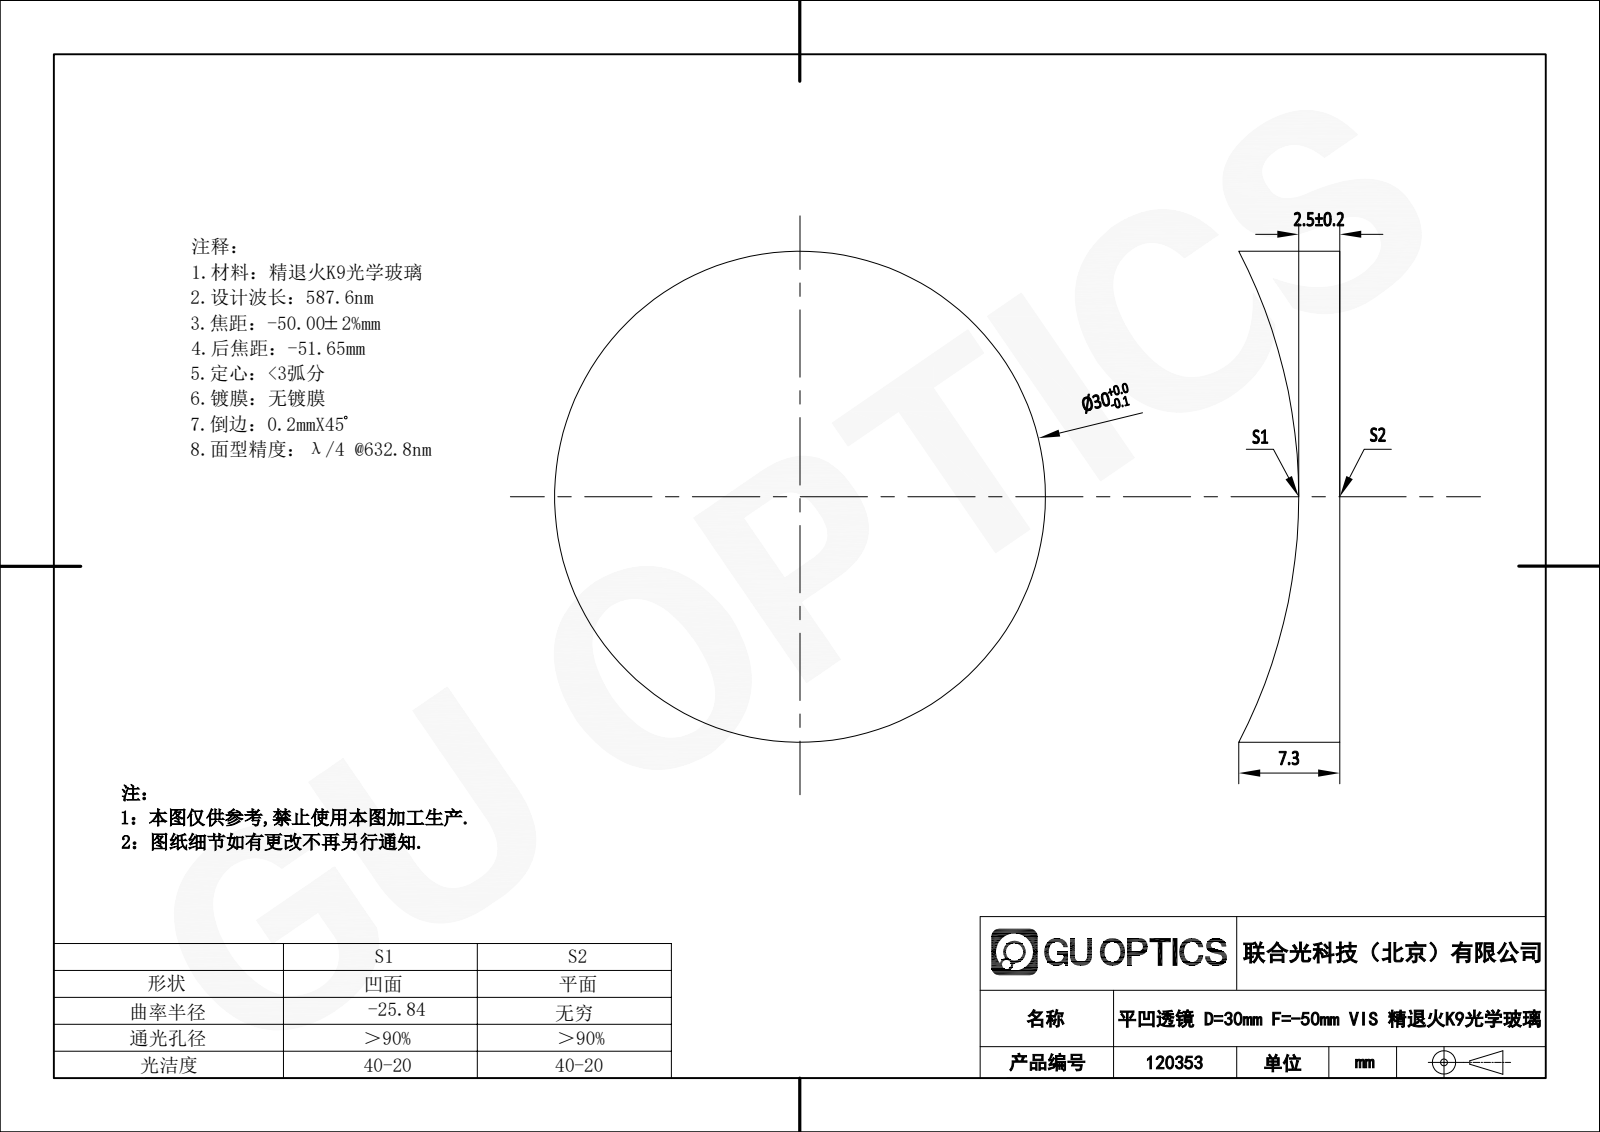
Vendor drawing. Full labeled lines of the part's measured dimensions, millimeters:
Part name (STEP PRODUCT): 120353
STEP written by: SolidWorks 2020 (CONFIG_CONTROL_DESIGN)
Units: millimetres
Bodies: 1 solid, 5 faces (1 planar, 2 cylindrical, 2 other)
Overall size (bounding box): 30 × 30 × 7.3
Volume: 3 406 mm³ · Surface area: 2 174 mm²
Round bosses / shafts (diameter × count): ⌀30 ×1
